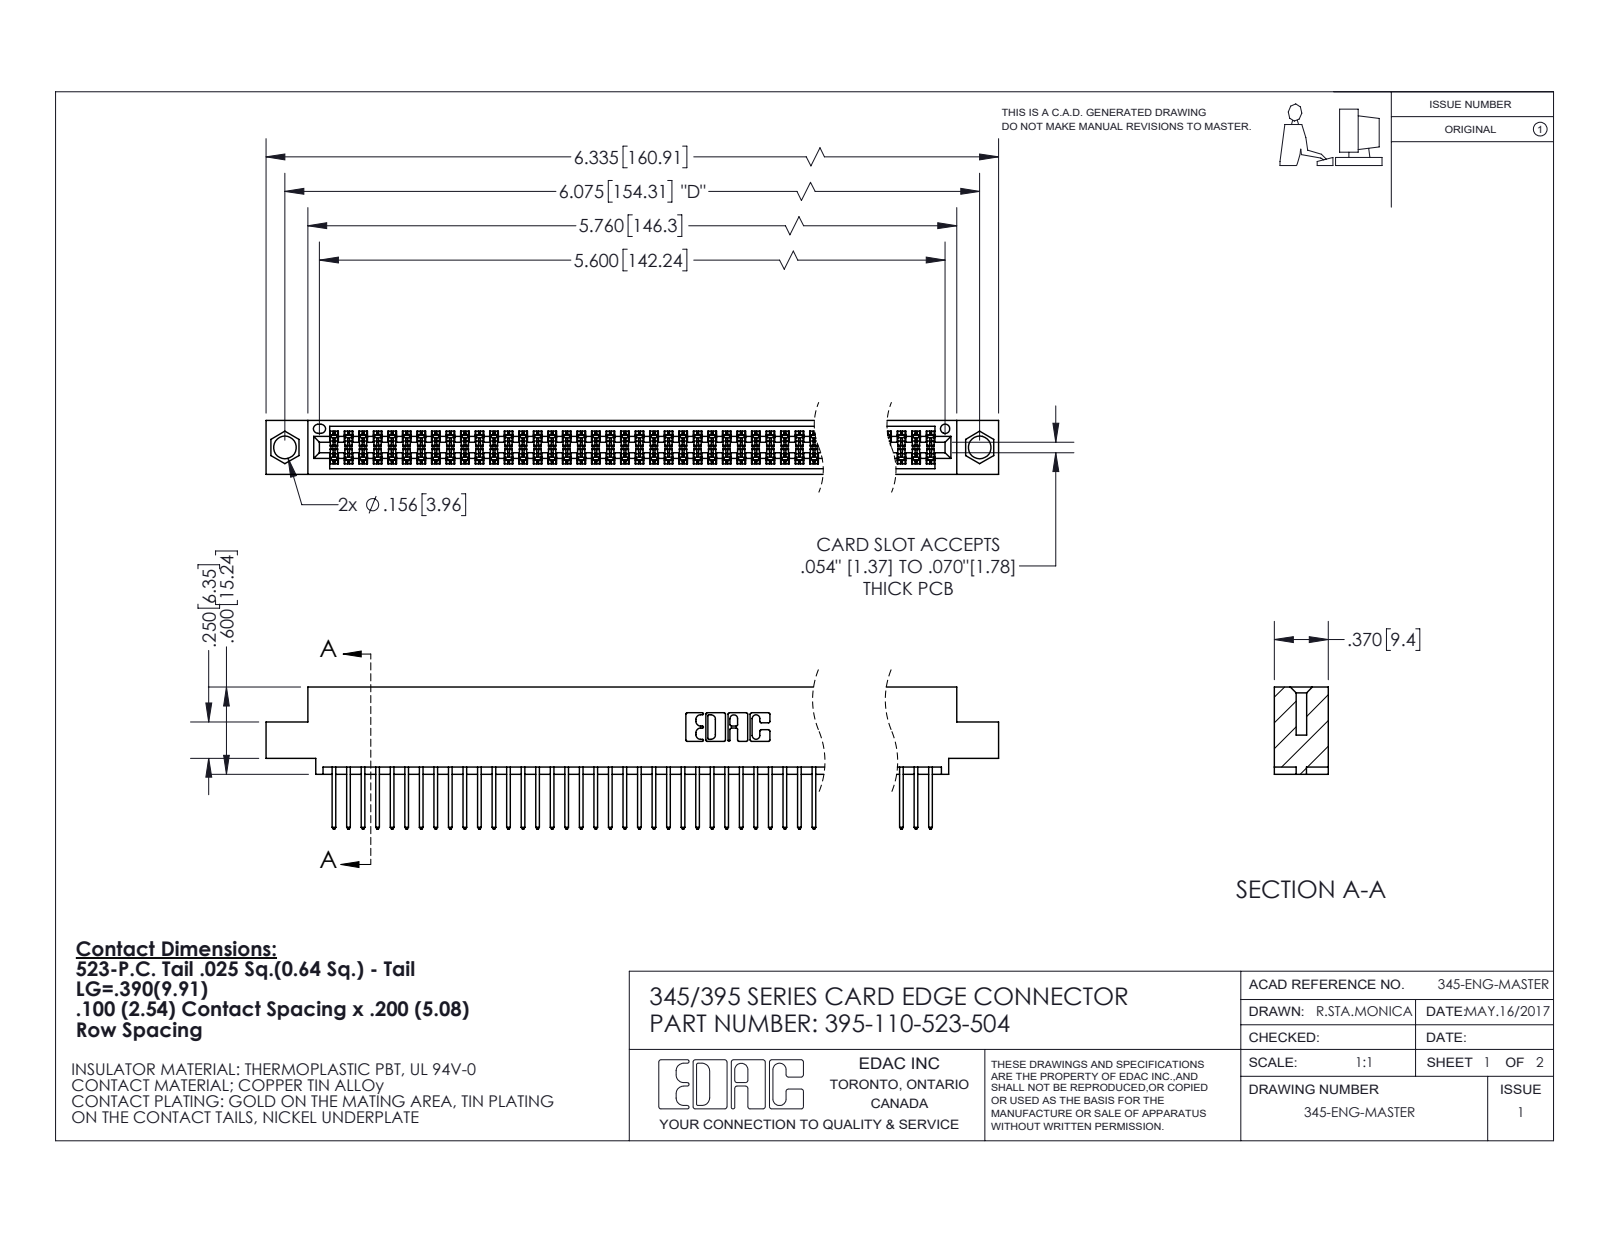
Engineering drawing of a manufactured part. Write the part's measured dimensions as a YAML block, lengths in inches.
part_name: "345 Part_0.110 Offset - 0.156 Dia-TI; 345-292-001_345-293-123; 395-110-523-504"
step_written_by: "SolidWorks 2020 (CONFIG_CONTROL_DESIGN)"
units: inches
bodies: {solids: 111, faces: 5644, planar: 3728, cylindrical: 1916, other: 0}
overall_size: [6.335, 0.977, 0.37]
volume: 0.964
surface_area: 38.07
round_holes:
  - {diameter: 0.156, count: 2}
  - {diameter: 0.064, count: 1}
partial_cylinders:
  - {radius: 0.006, count: 165}
  - {radius: 0.01, count: 110}
  - {radius: 0.01, count: 22}
  - {radius: 0.007, count: 6}
  - {radius: 0.031, count: 6}
  - {radius: 0.026, count: 3}
  - {radius: 0.014, count: 2}
  - {radius: 0.019, count: 2}
face_to_face_distances: [0.298, 0.072, 0.2, 0.098, 0.272, 0.025, 0.37, 0.225, 0.175, 0.149]
hole_center_spacings: [0.27, 5.839, 6.075]
